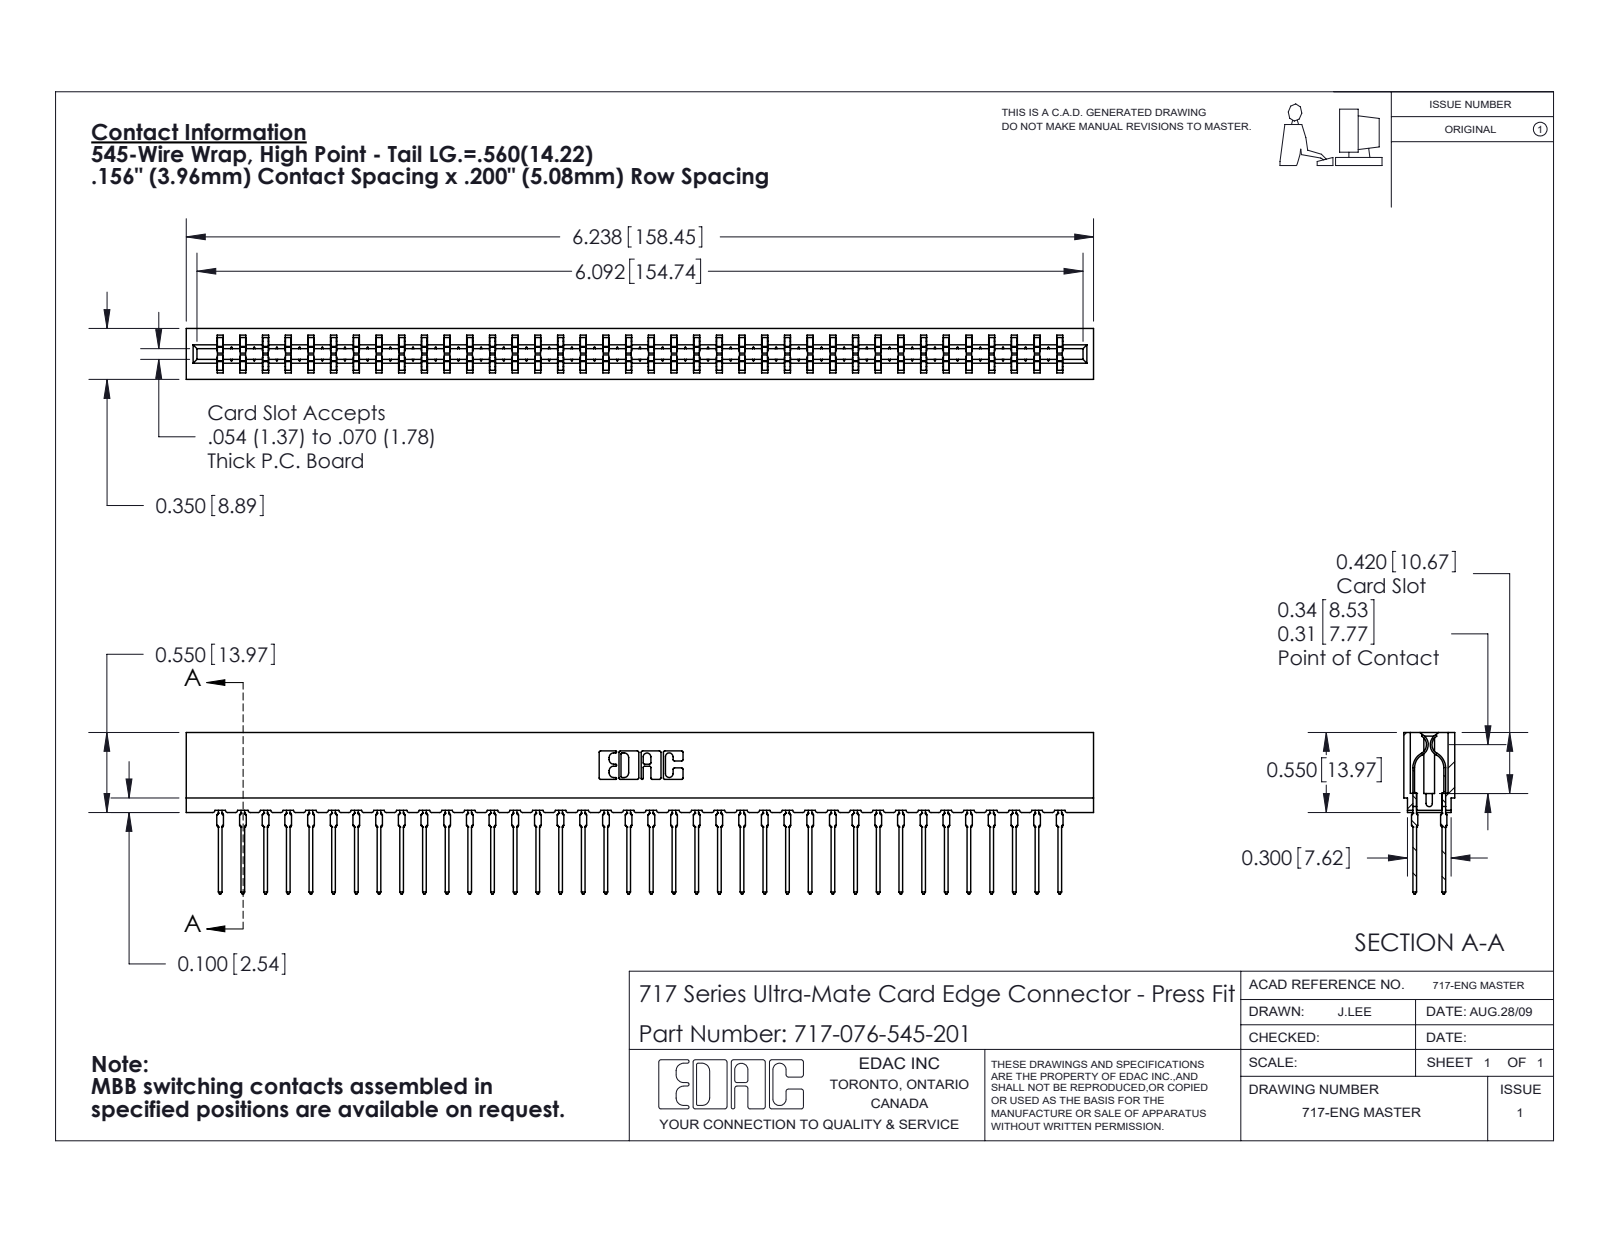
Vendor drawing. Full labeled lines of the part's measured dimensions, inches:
Part name (STEP PRODUCT): 717 Part_Insulator Option - 06; 717-076-545-201; 745-292-001_545
STEP written by: SolidWorks 2020 (CONFIG_CONTROL_DESIGN)
Units: inches
Bodies: 77 solids, 6934 faces (3588 planar, 1370 cylindrical, 1976 other)
Overall size (bounding box): 6.238 × 1.109 × 0.35
Volume: 0.855 in³ · Surface area: 35.14 in²
Partial cylindrical surfaces — rounded edges, fillets, slot ends (radius × count): R0.021 ×152, R0.015 ×76, R0.01 ×22, R0.005 ×8, R0.011 ×8, R0.007 ×6, R0.031 ×6, R0.026 ×3
Main face-to-face distances: 0.212, 0.138, 0.35, 0.063, 0.287, 0.076, 0.149, 0.074, 0.087, 0.263
